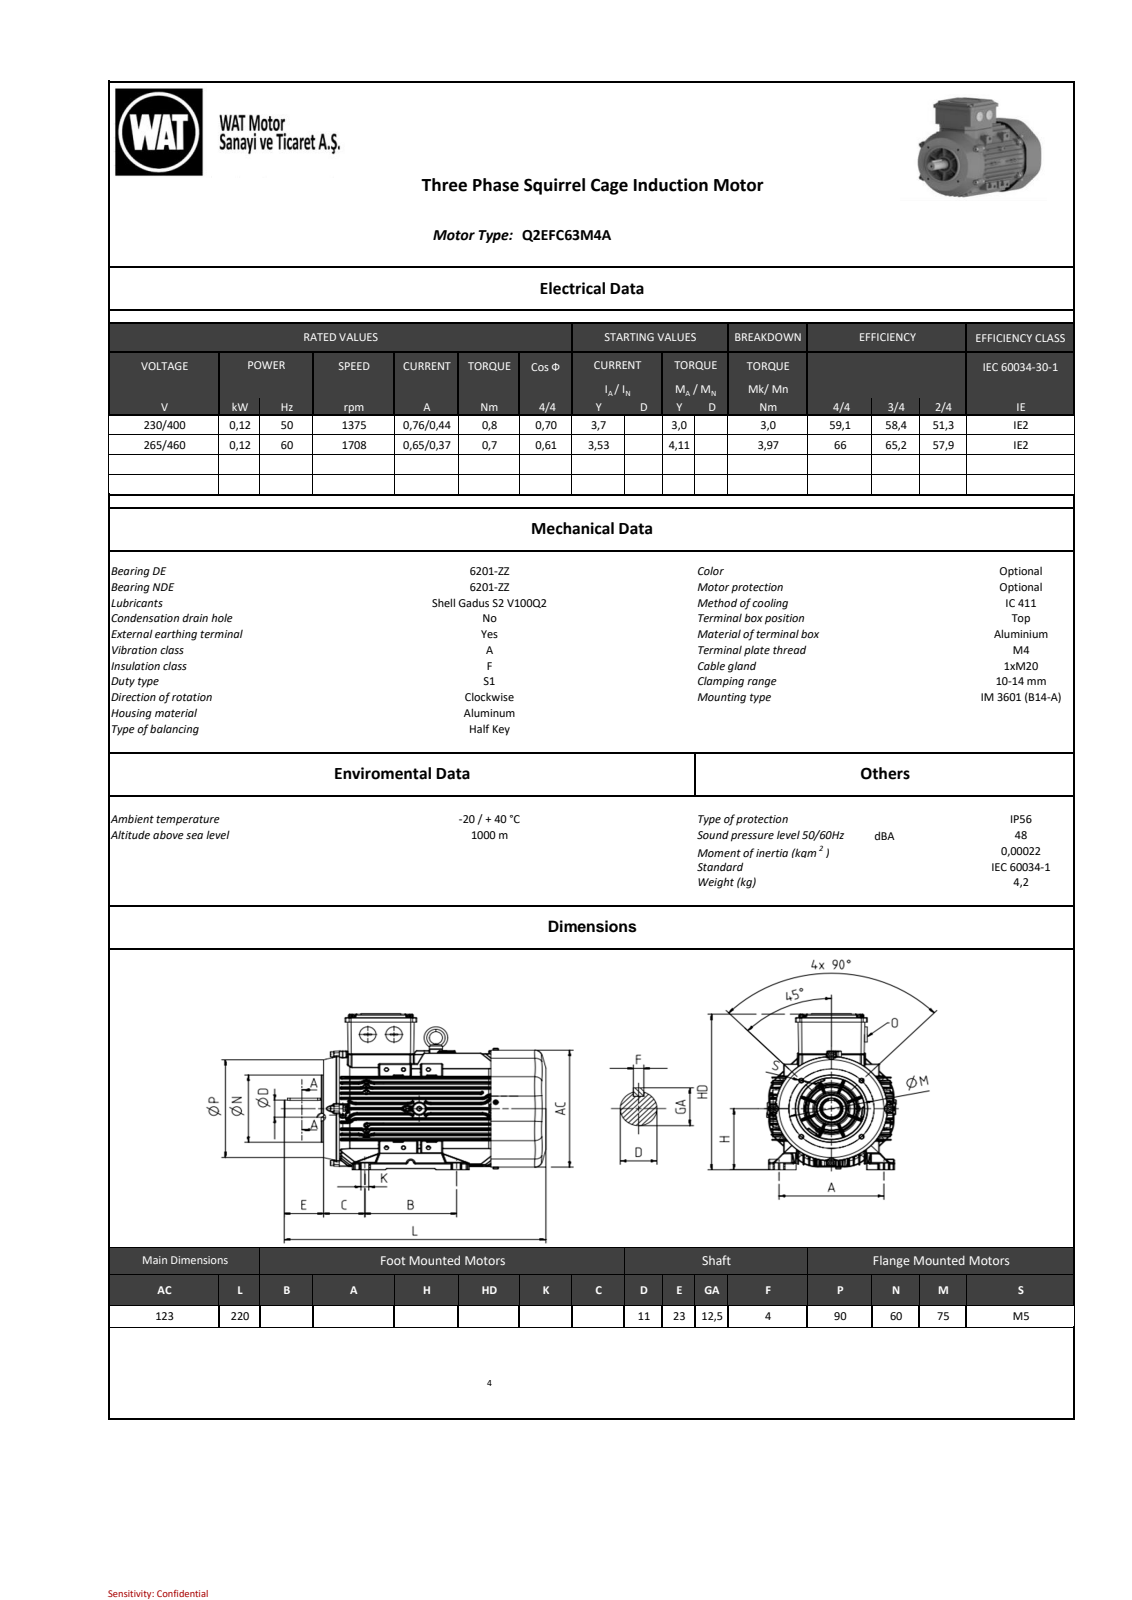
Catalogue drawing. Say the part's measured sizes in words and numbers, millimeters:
The part is named "QSFC63GMM". Its 3-D file was written by "UNIX (AUTOMOTIVE_DESIGN)". It is 8 solids with 2517 faces: 0 planar, 0 cylindrical and 2517 other. Overall it measures 219.14 by 159.6 by 128 millimeters. Its volume is 27 685 cubic millimeters and its surface area 362 448 square millimeters.
